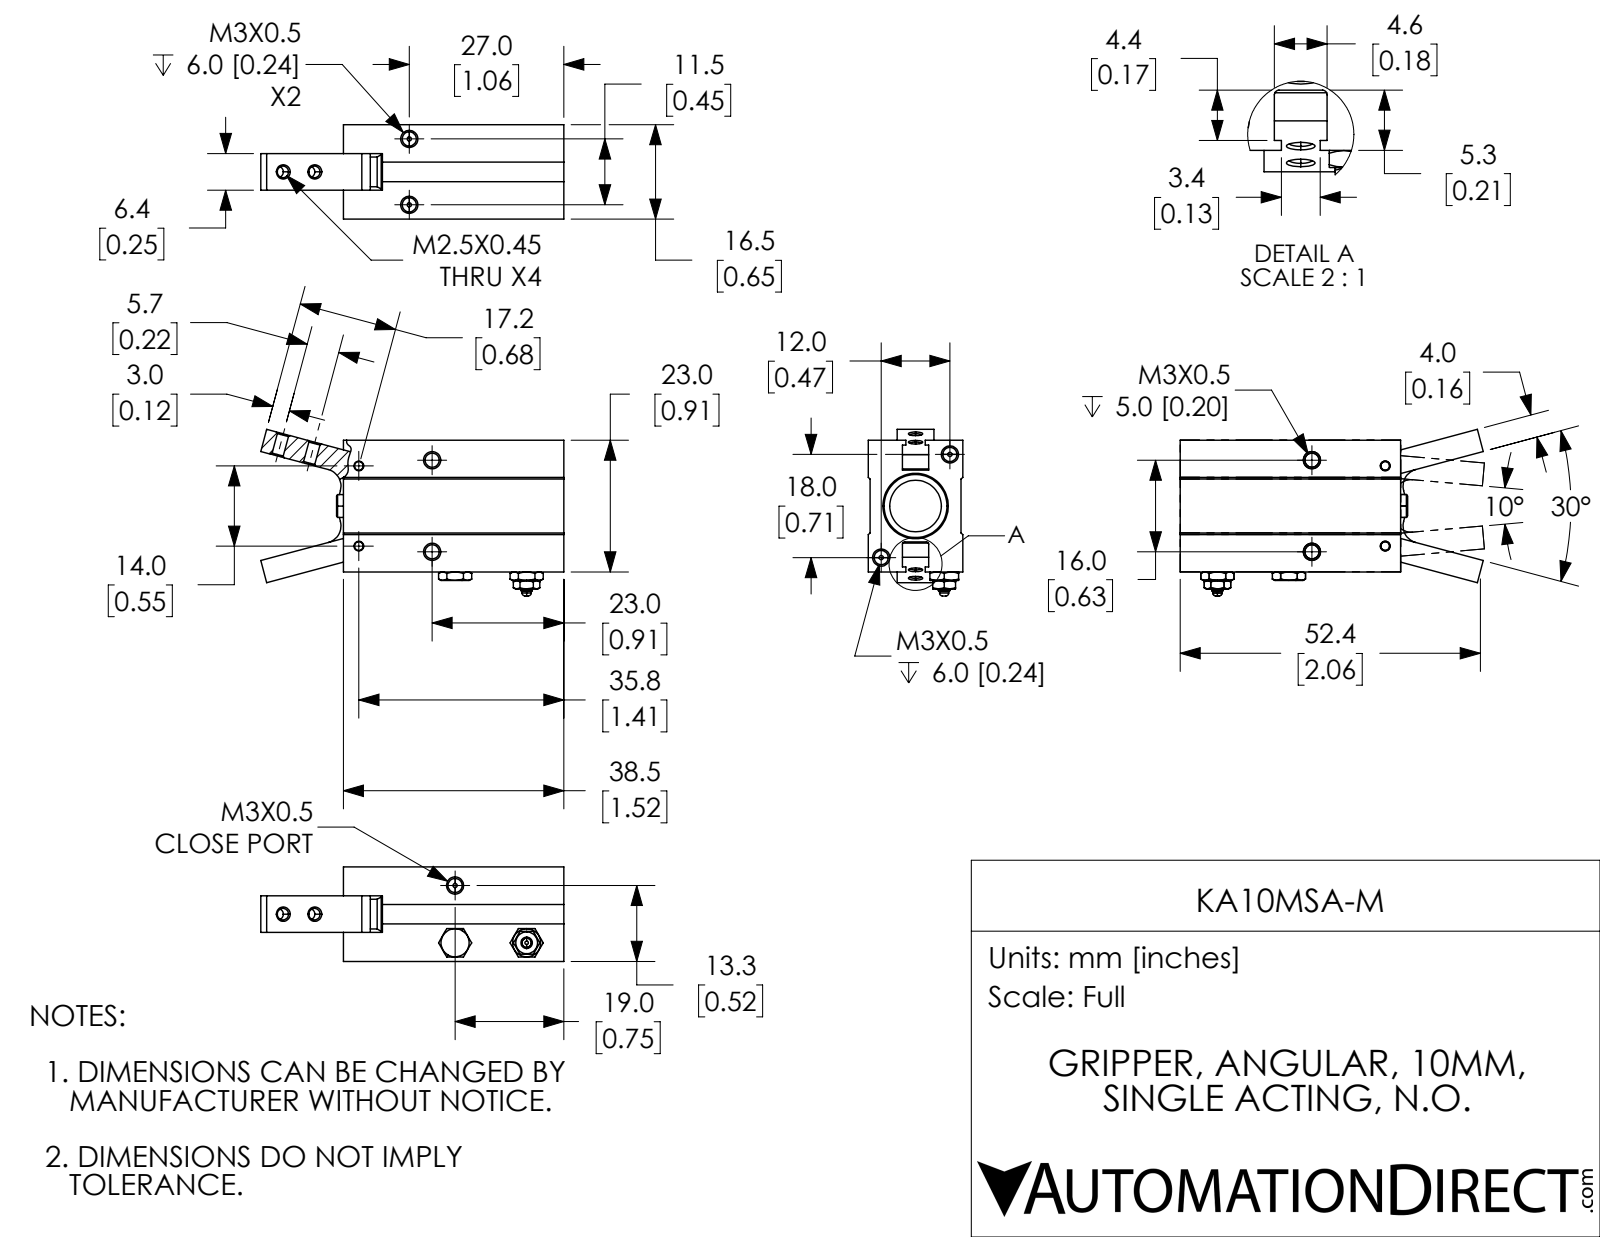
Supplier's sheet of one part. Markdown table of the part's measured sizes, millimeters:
| quantity | value |
| --- | --- |
| part name | KA10MSA-M-1; KA10MSA-M; KA10MSA-M-3; KA10MSA-M-2 (+1 more) |
| STEP written by | SolidWorks 2017 (AUTOMOTIVE_DESIGN) |
| units | millimeters |
| bodies | 4 solids, 274 faces (108 planar, 86 cylindrical, 80 other) |
| overall size | 52.93 × 29.08 × 16.5 |
| volume | 11 798 mm³ |
| surface area | 8 380 mm² |
| round holes (diameter × count) | 2.46 × 4, 2.46 × 4, 1.5 × 3, 2.01 × 2, 2.01 × 2, 3.2 × 2, 6 × 1, 9 × 1, 10 × 1, 11 × 1, 12 × 1 |
| round bosses / shafts (diameter × count) | 9.9 × 1, 5.2 × 1, 4 × 1, 2 × 1, 1.6 × 1 |
| partial cylindrical surfaces (radius × count) | 0.4 × 2, 2 × 2, 3 × 2 |
| main face-to-face distances | 16.2, 5.65, 5.95, 10.55, 10.25, 5.5, 11.15, 16.5, 5.05, 11.45 |
| hole center spacings | 5.7, 7.25, 8.04, 10.82, 12.84, 13.4, 16.74, 19.72 |
